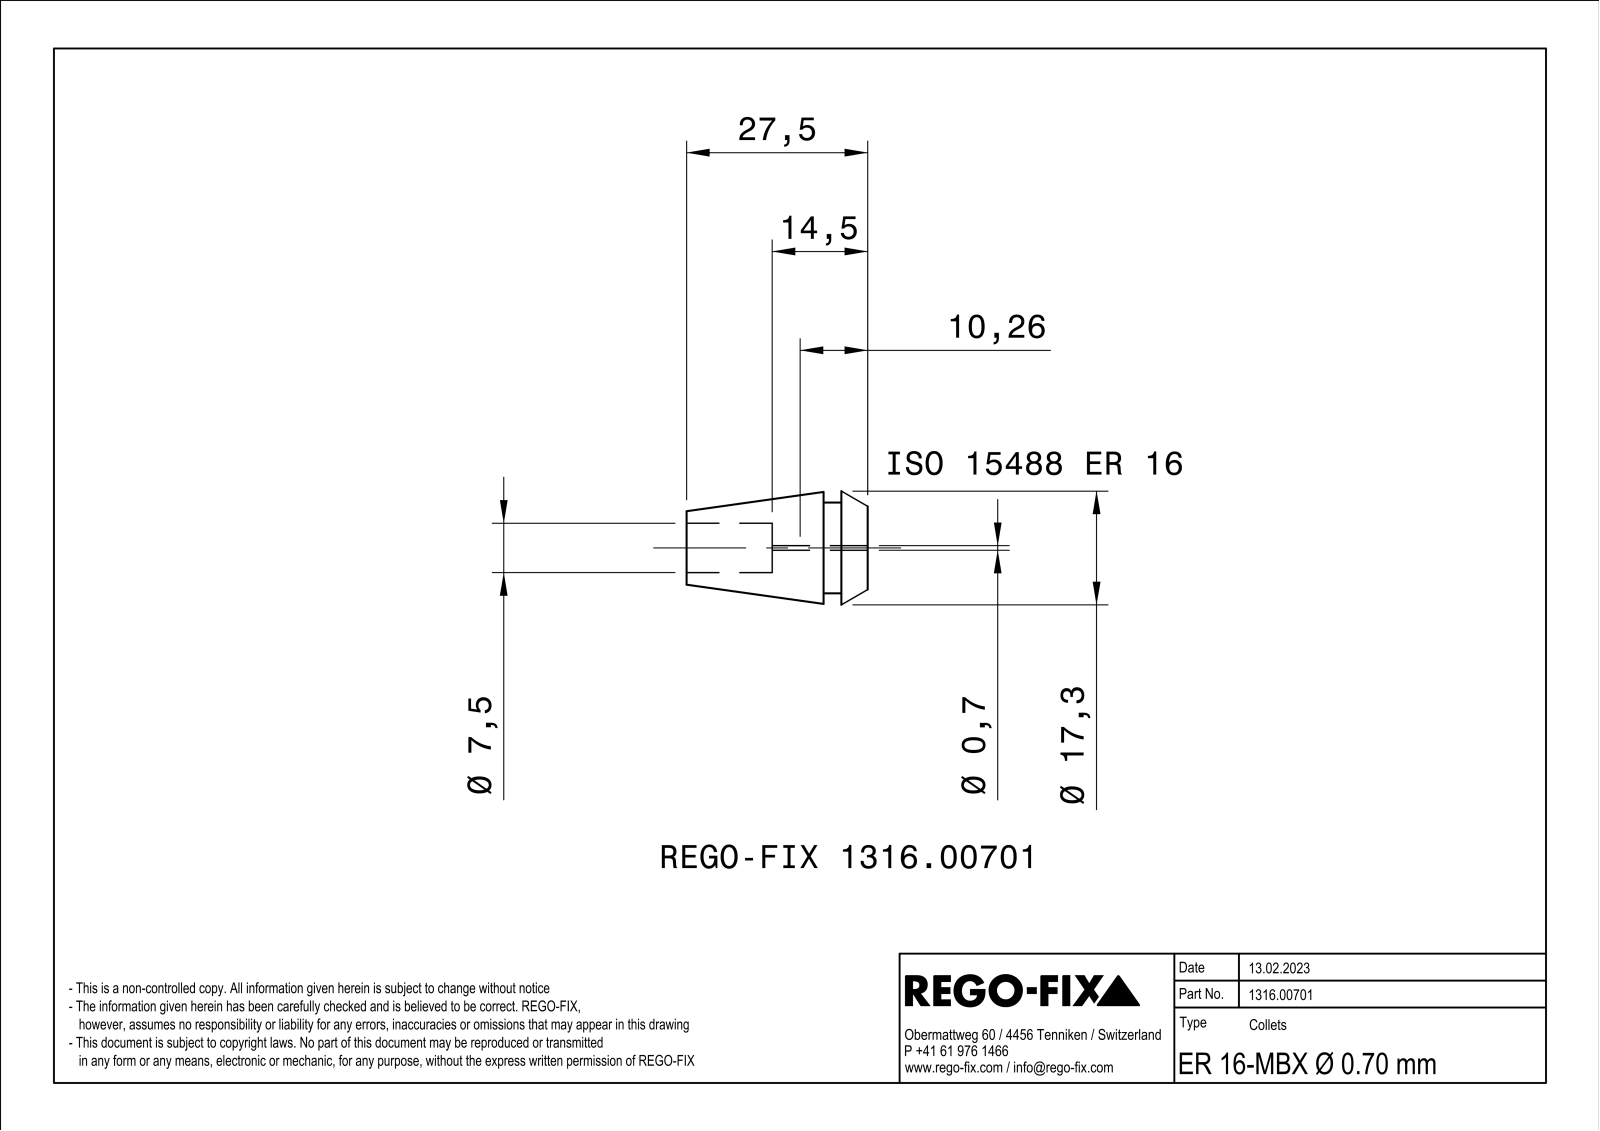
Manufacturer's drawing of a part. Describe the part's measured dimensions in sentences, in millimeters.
The part is named "NOCUT". Its 3-D file was written by "SIEMENS PLM Software Solid Edge ST10 (AUTOMOTIVE_DESIGN)". It is 1 solid with 109 faces: 36 planar, 27 cylindrical and 46 other. Overall it measures 27.5 by 16.91 by 16.9 millimeters. Its volume is 3 318 cubic millimeters and its surface area 3 326 square millimeters. Round holes: 3 of diameter 2, 1 of diameter 7.5. Round bosses or shafts: 1 of diameter 13.8. Partial cylindrical surfaces (rounded edges, fillets, slot ends): 3 of radius 0.11, 3 of radius 25, 1 of radius 0.35. The main face-to-face distances are 0.51, 0.8, 6.7, 4, 2.7, 27.5, 23.5, 20.8, 14.5, 10.5. The hole center spacings are 2.1, 3.64.
